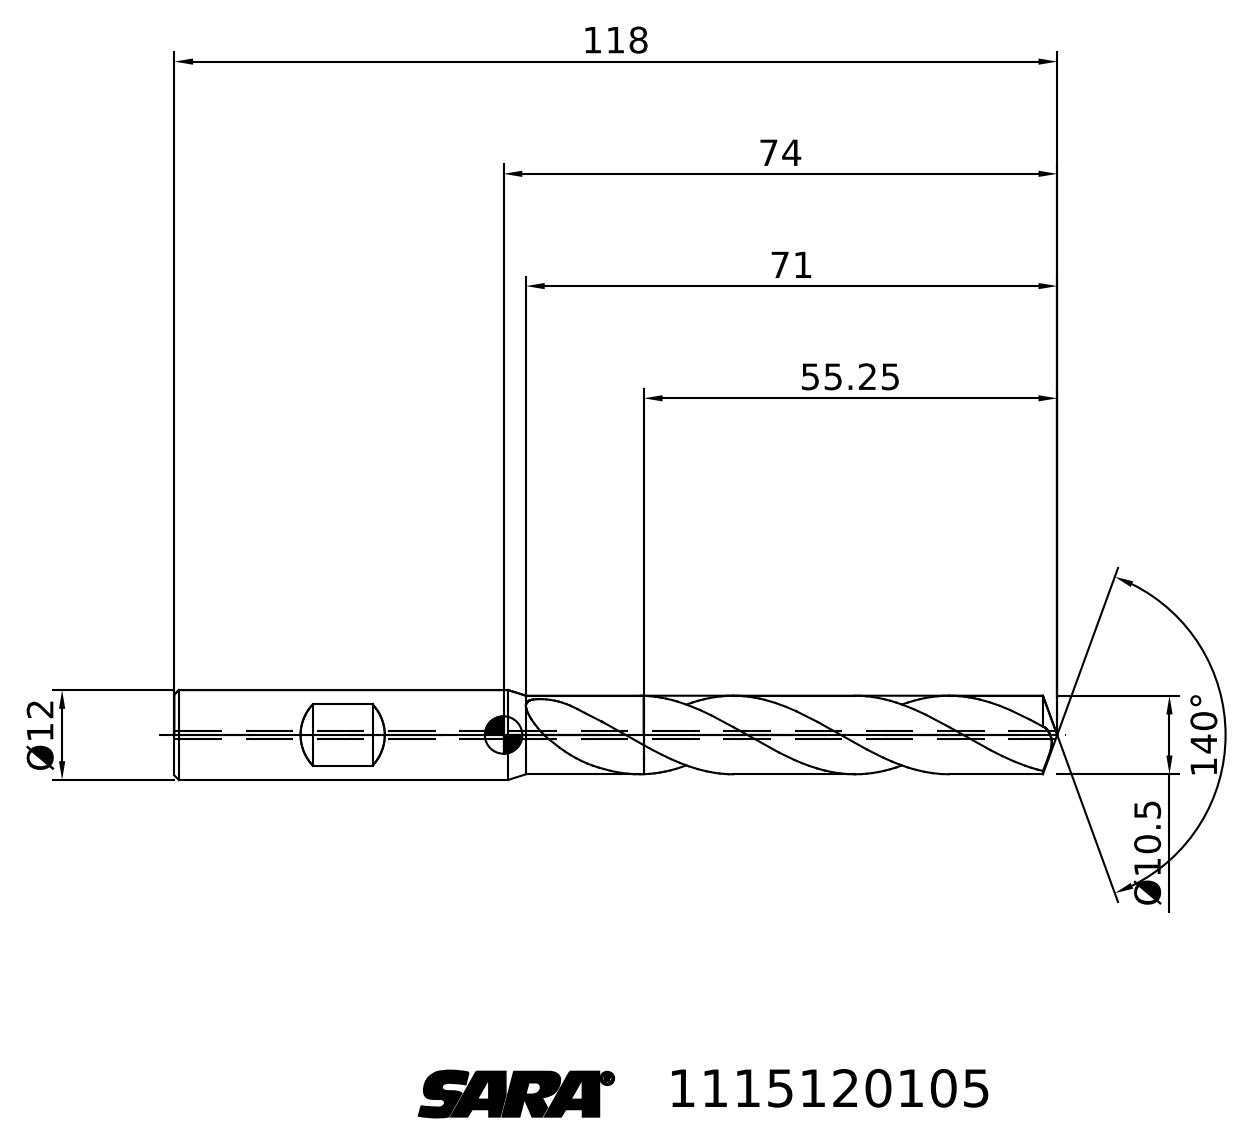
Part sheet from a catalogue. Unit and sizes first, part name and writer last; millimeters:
Units: millimetres
Overall size (bounding box): 118 × 27.67 × 16.15
Main face-to-face distances: 62.75
Volume: 9 250 mm³ · Surface area: 4 543 mm²
Bodies: 2 solids, 29 faces (6 planar, 0 cylindrical, 23 other)
STEP written by: TDM (AUTOMOTIVE_DESIGN)
